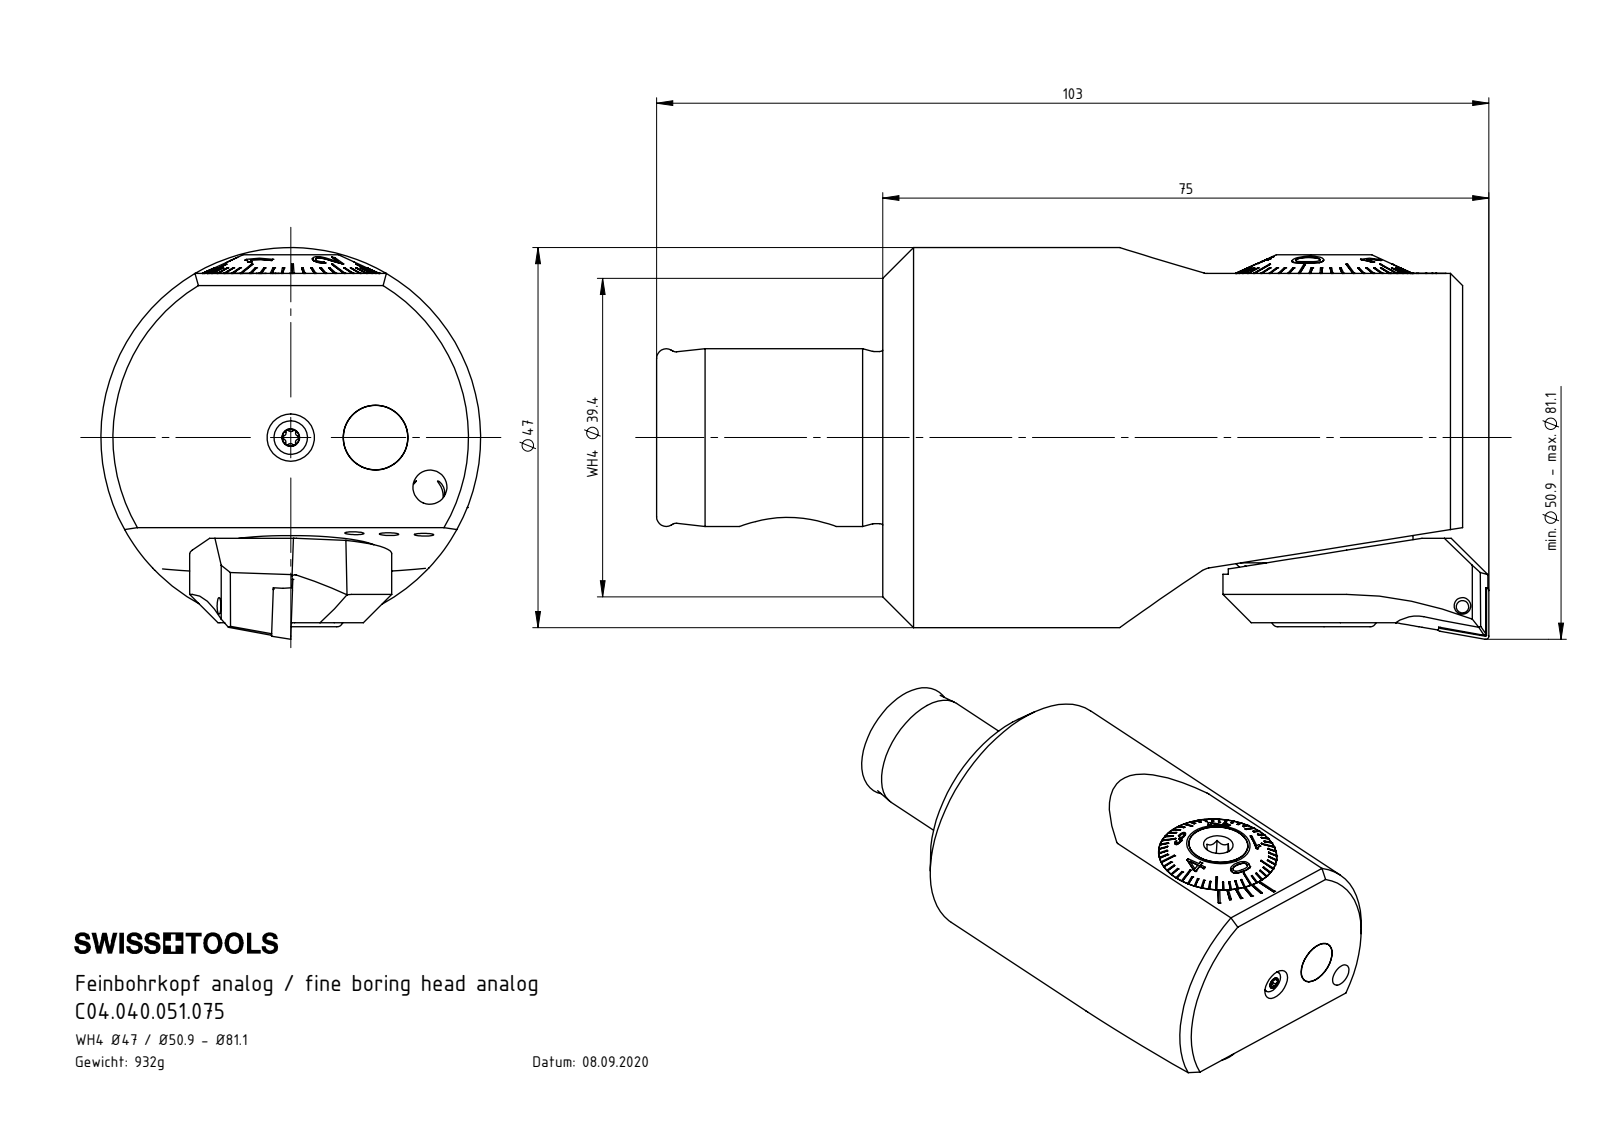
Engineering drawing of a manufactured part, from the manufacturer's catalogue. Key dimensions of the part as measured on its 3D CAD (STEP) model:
Part name (STEP PRODUCT): A42-BG2.013.005_B; ISO 4026 - M8 x 8_fr.step; WH4-F42.AA3.075_A; WCA-ER2.001.007_A (+8 more)
STEP written by: SolidWorks 2017 (CONFIG_CONTROL_DESIGN)
Units: millimetres
Bodies: 13 solids, 692 faces (300 planar, 130 cylindrical, 262 other)
Overall size (bounding box): 99.75 × 47 × 47
Volume: 117 001 mm³ · Surface area: 30 173 mm²
Round holes (diameter × count): ⌀2.1 ×3, ⌀4.2 ×2, ⌀6.8 ×2, ⌀8.5 ×2, ⌀2.5 ×1, ⌀3 ×1, ⌀3.2 ×1, ⌀3.3 ×1, ⌀3.9 ×1, ⌀4 ×1, ⌀6 ×1, ⌀8 ×1
Round bosses / shafts (diameter × count): ⌀22 ×2, ⌀8 ×2, ⌀47 ×1, ⌀21.98 ×1, ⌀21.9 ×1, ⌀21.3 ×1, ⌀18.45 ×1, ⌀13 ×1
Partial cylindrical surfaces — rounded edges, fillets, slot ends (radius × count): R0.21 ×6, R0.36 ×5, R1.4 ×4, R0.5 ×3, R3.2 ×3, R2 ×2, R0.36 ×1, R2.5 ×1
Main face-to-face distances: 71.75, 5.6, 2.2, 4.5, 1.1, 2.3, 3.3, 30.6, 35.1, 36.2
Hole centre spacings: 10.5, 12.33
